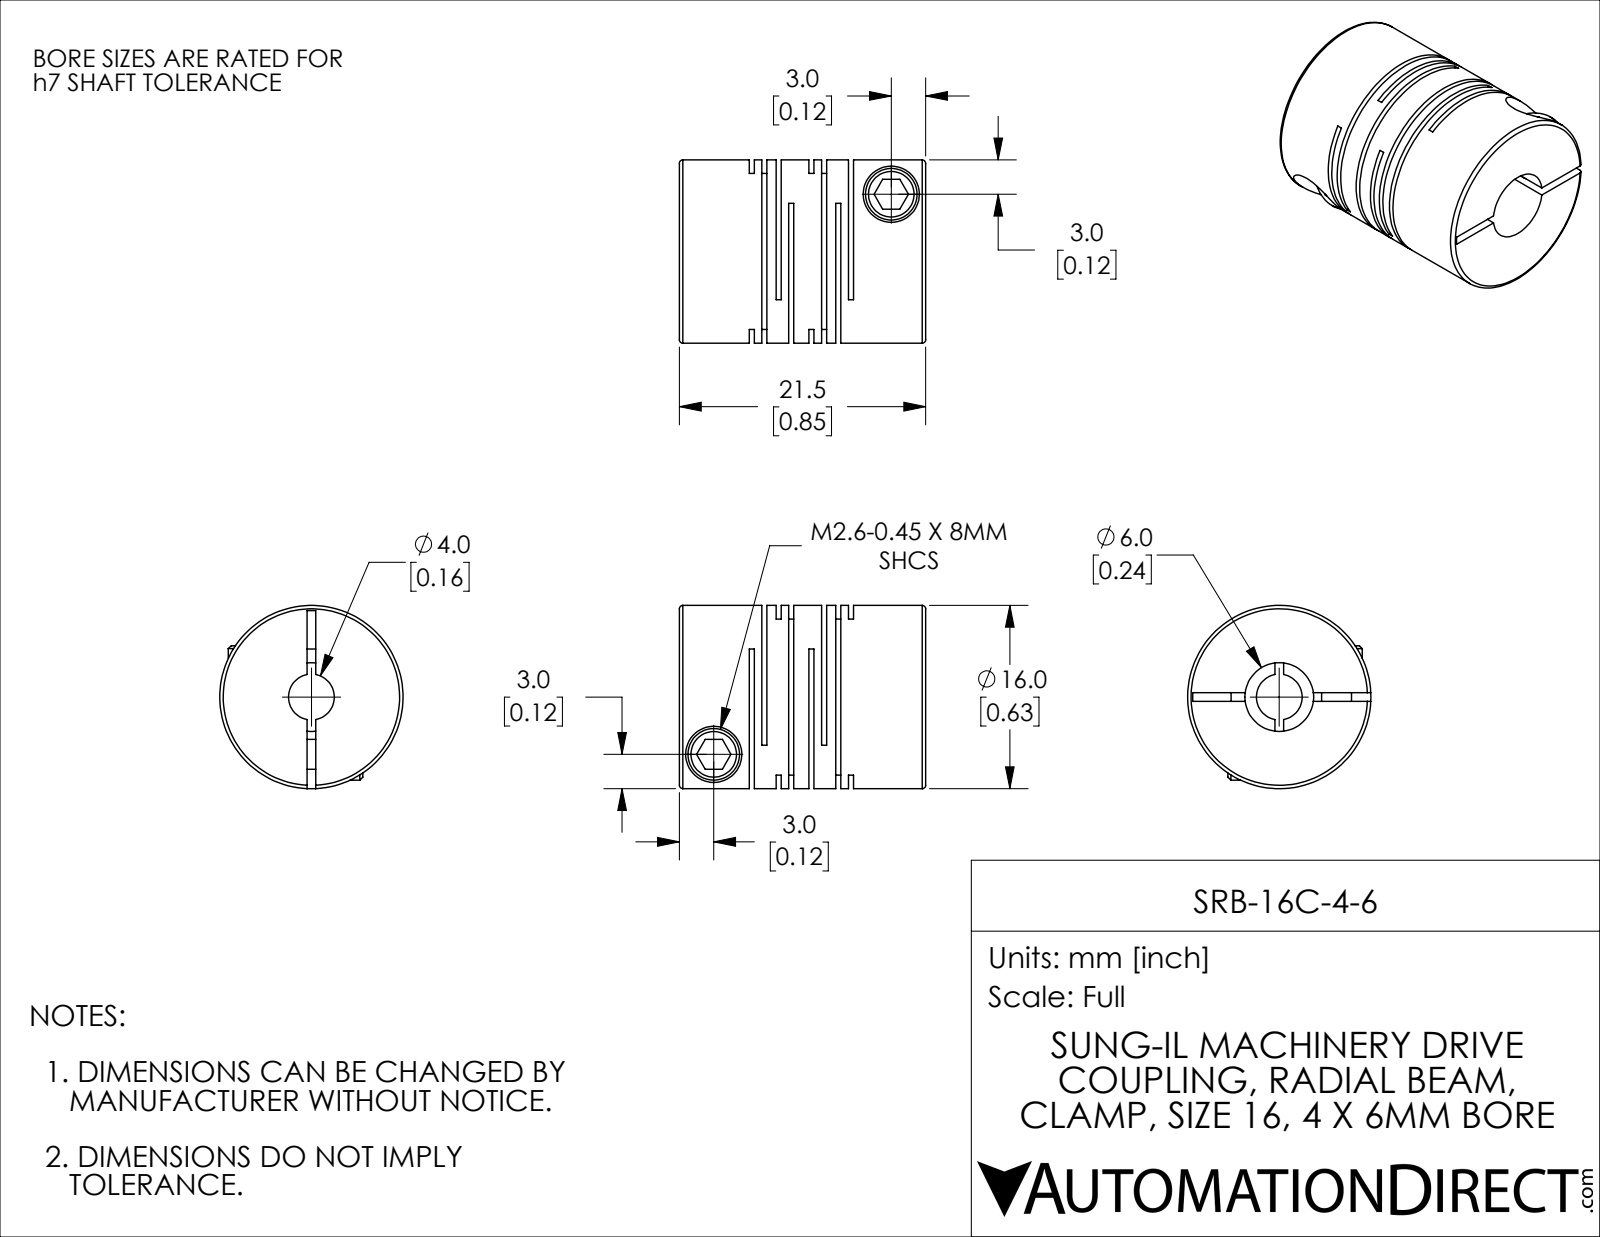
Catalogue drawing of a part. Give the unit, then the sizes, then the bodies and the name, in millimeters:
Units: millimetres
Overall size (bounding box): 21.5 × 16 × 16
Round holes (diameter × count): ⌀2.6 ×2, ⌀4.9 ×2, ⌀4 ×1, ⌀6 ×1
Round bosses / shafts (diameter × count): ⌀4.5 ×2, ⌀16 ×1
Main face-to-face distances: 0.44, 1.1, 2.35, 5.21, 0.66, 1.91, 4.77, 1.25, 4.11, 2.86
Volume: 3 139 mm³ · Surface area: 4 258 mm²
Bodies: 1 solid, 114 faces (60 planar, 42 cylindrical, 12 other)
Part name (STEP PRODUCT): SRB-16C-4-6
STEP written by: SolidWorks 2021 (CONFIG_CONTROL_DESIGN)
